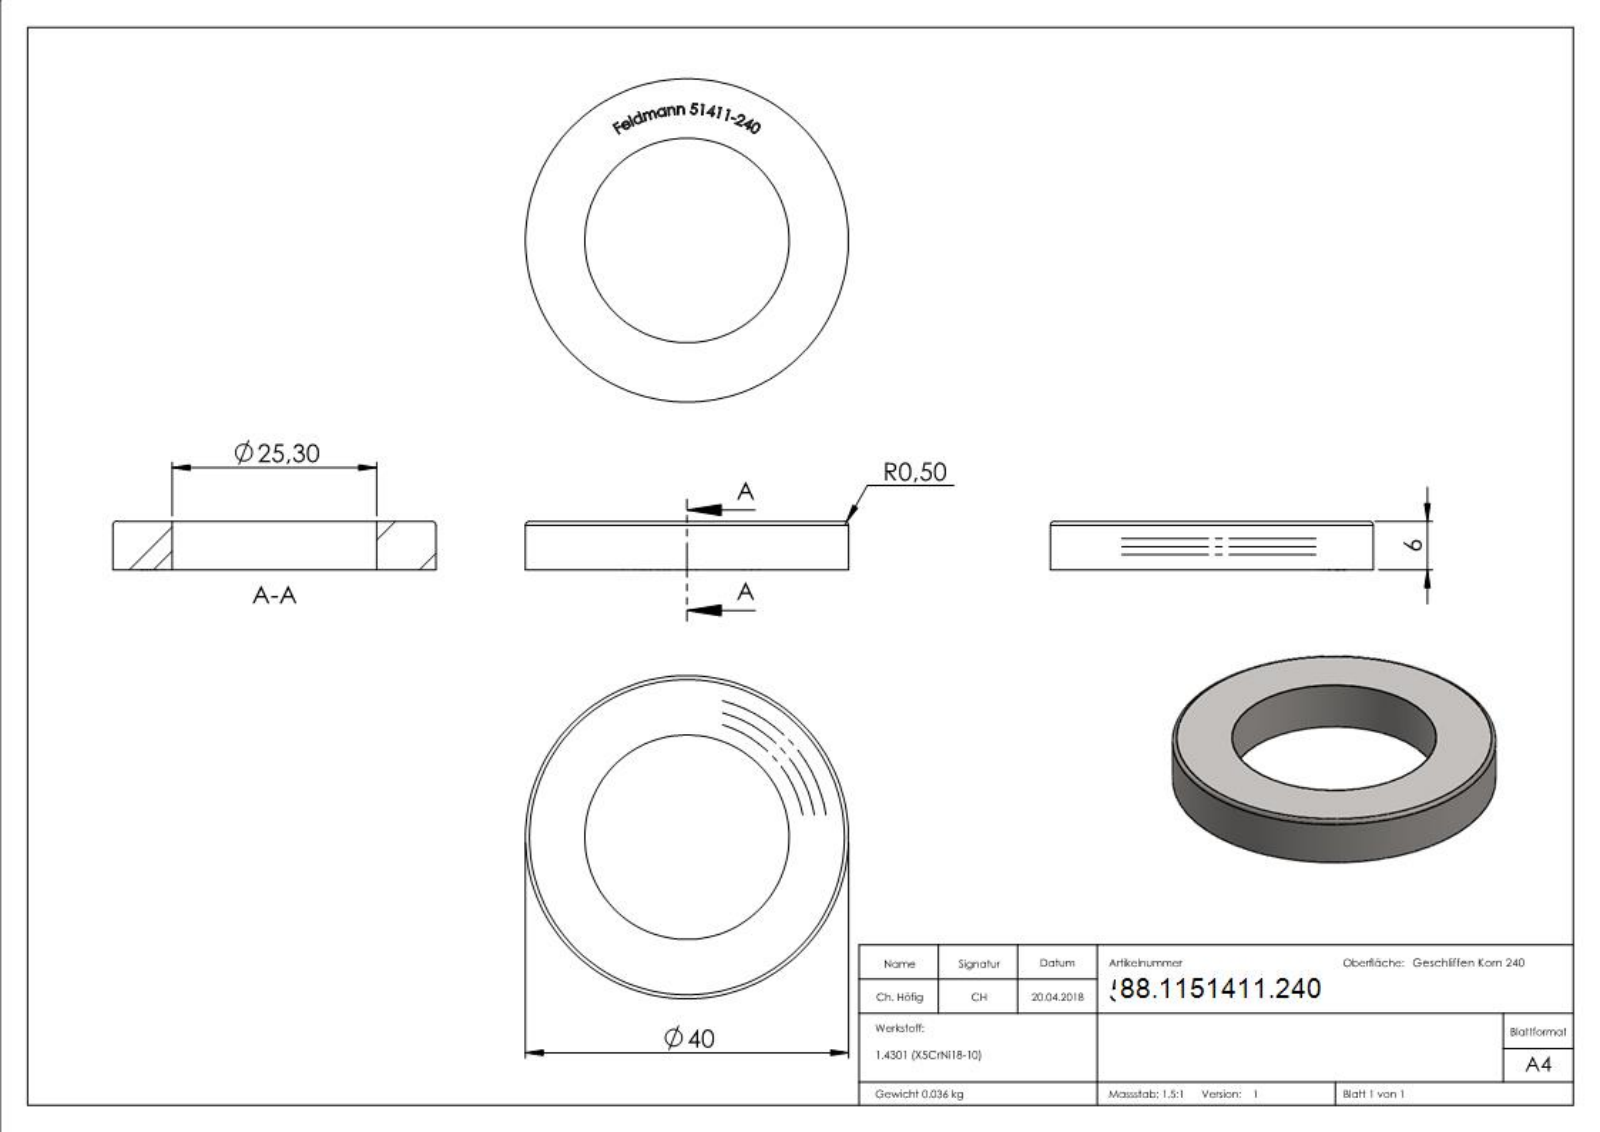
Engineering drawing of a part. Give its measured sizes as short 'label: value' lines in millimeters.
name: 51411-240
written by: SolidWorks 2018 (CONFIG_CONTROL_DESIGN)
unit: mm
bodies: 1 solid, 213 faces (139 planar, 2 cylindrical, 72 other)
size: 40 × 40 × 6
volume: 4 516 mm³; area: 2 720 mm²
holes: 1× ⌀25.3
bosses: 1× ⌀40
face distances: 6, 5.9, 0.72, 0.85, 0.54, 0.67, 0.66, 1.46, 1.33, 0.41
